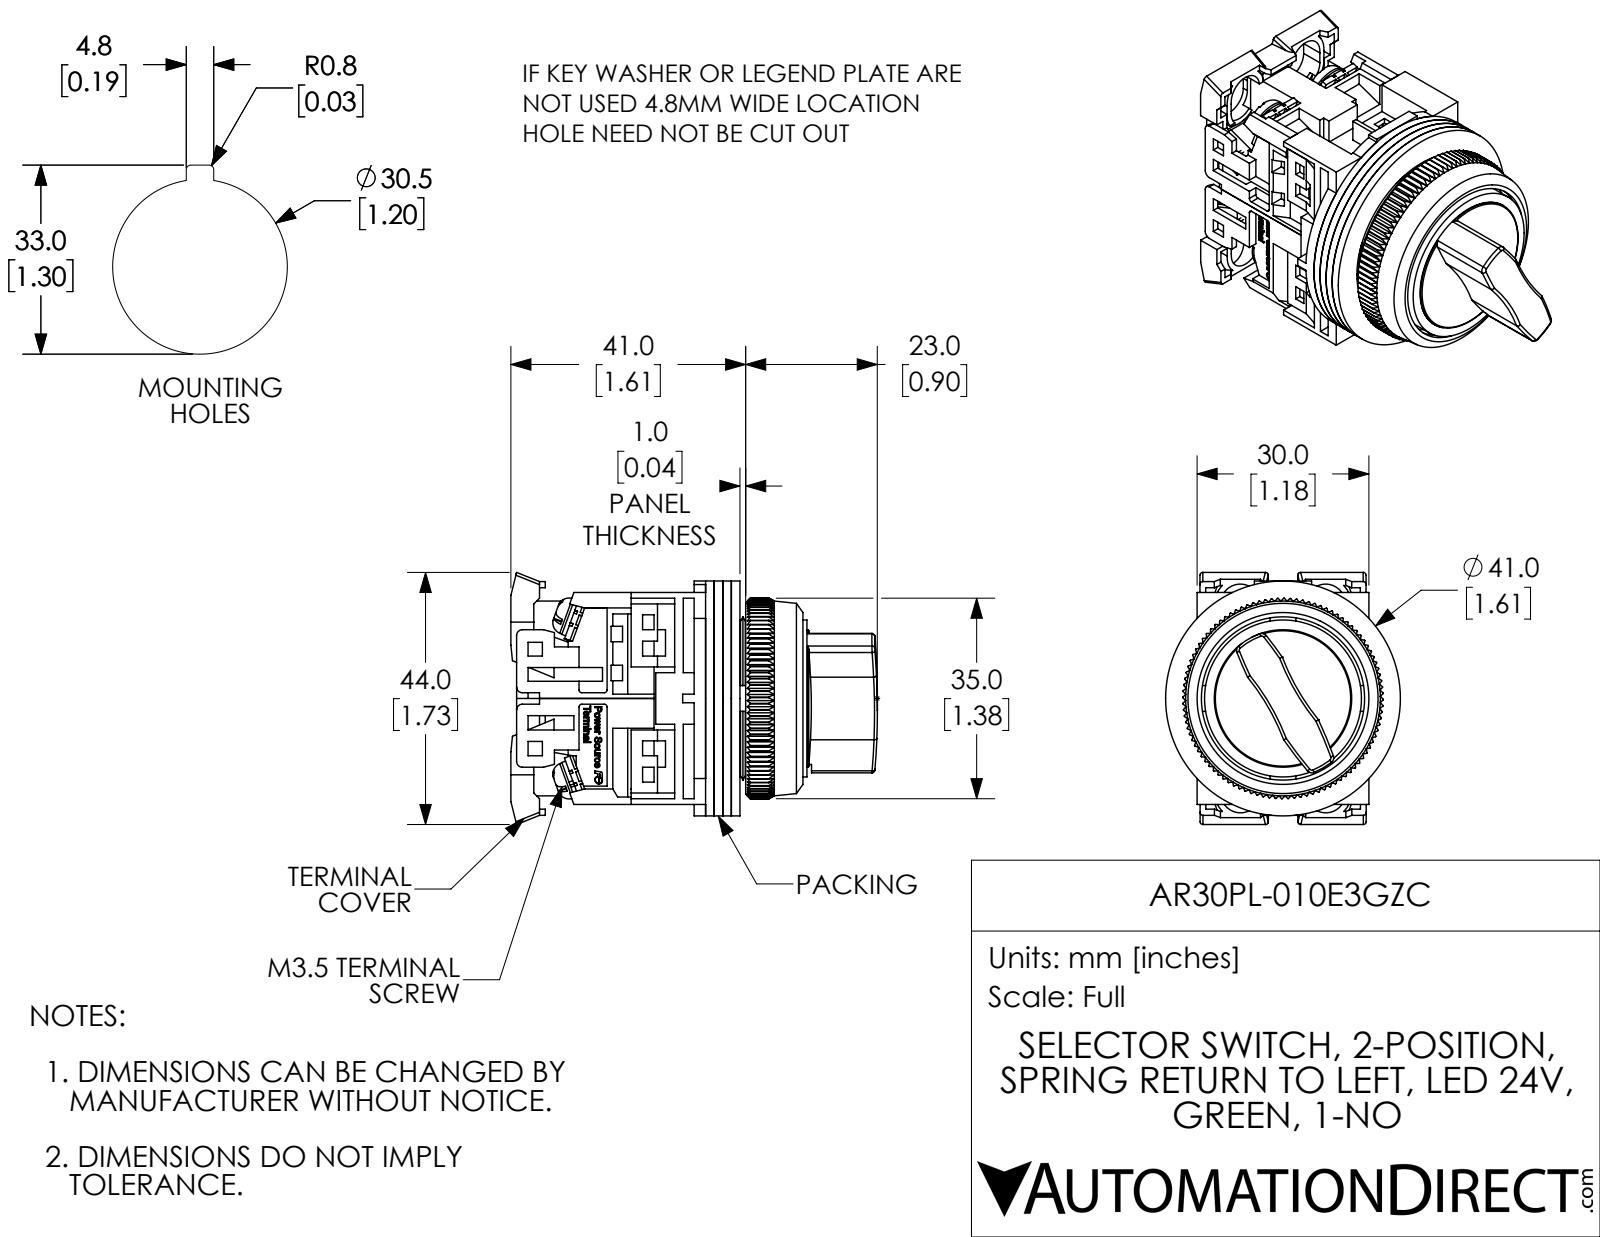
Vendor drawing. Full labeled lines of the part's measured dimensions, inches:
Part name (STEP PRODUCT): AR30PL-010E3GZC
STEP written by: SolidWorks 2017 (AUTOMOTIVE_DESIGN)
Units: inches
Bodies: 25 solids, 2434 faces (1731 planar, 305 cylindrical, 398 other)
Overall size (bounding box): 2.52 × 1.732 × 1.614
Volume: 2.238 in³ · Surface area: 59.31 in²
Round holes (diameter × count): ⌀0.138 ×8, ⌀0.142 ×4, ⌀0.118 ×1, ⌀0.472 ×1, ⌀0.709 ×1, ⌀0.768 ×1, ⌀0.827 ×1, ⌀1.122 ×1, ⌀1.181 ×1, ⌀1.252 ×1
Round bosses / shafts (diameter × count): ⌀0.26 ×4, ⌀0.138 ×4, ⌀0.063 ×2, ⌀1.614 ×1, ⌀1.15 ×1, ⌀1.079 ×1, ⌀0.945 ×1, ⌀0.886 ×1
Partial cylindrical surfaces — rounded edges, fillets, slot ends (radius × count): R0.059 ×16, R0.02 ×12, R0.039 ×8, R0.138 ×4, R0.177 ×4, R0.118 ×2, R1.575 ×2, R2.953 ×2
Main face-to-face distances: 0.059, 0.118, 0.177, 0.039, 0.079, 1.417, 1.358, 0.811, 0.197, 0.02
Hole centre spacings: 0.579, 0.61
